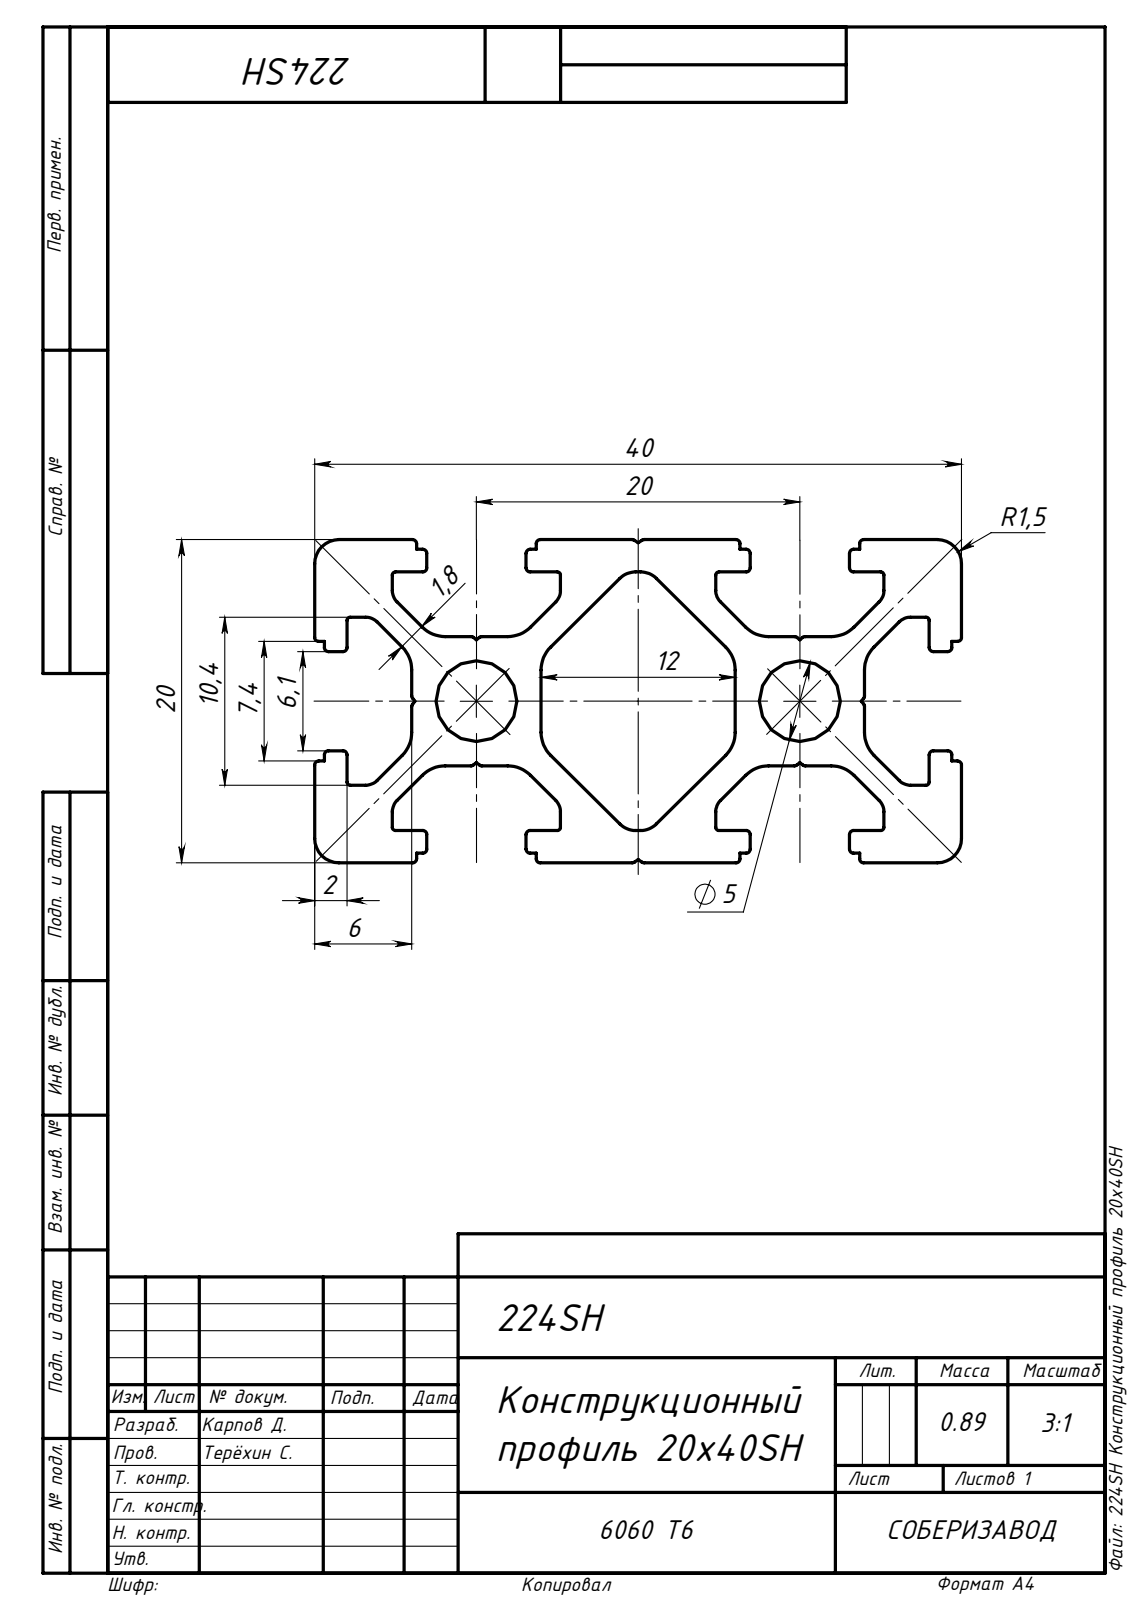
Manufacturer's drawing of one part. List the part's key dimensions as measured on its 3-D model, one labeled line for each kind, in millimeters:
STEP written by: SolidWorks 2018 (AUTOMOTIVE_DESIGN)
Units: millimetres
Bodies: 1 solid, 226 faces (122 planar, 104 cylindrical, 0 other)
Overall size (bounding box): 1000 × 40 × 20
Volume: 330 855 mm³ · Surface area: 293 133 mm²
Round holes (diameter × count): ⌀5 ×2
Partial cylindrical surfaces — rounded edges, fillets, slot ends (radius × count): R0.25 ×52, R2 ×16, R0.2 ×12, R1 ×12, R1.4 ×4, R1.5 ×4
Main face-to-face distances: 20, 12, 2, 14, 6, 4, 18, 8, 12.36, 1.2
Hole centre spacings: 20
